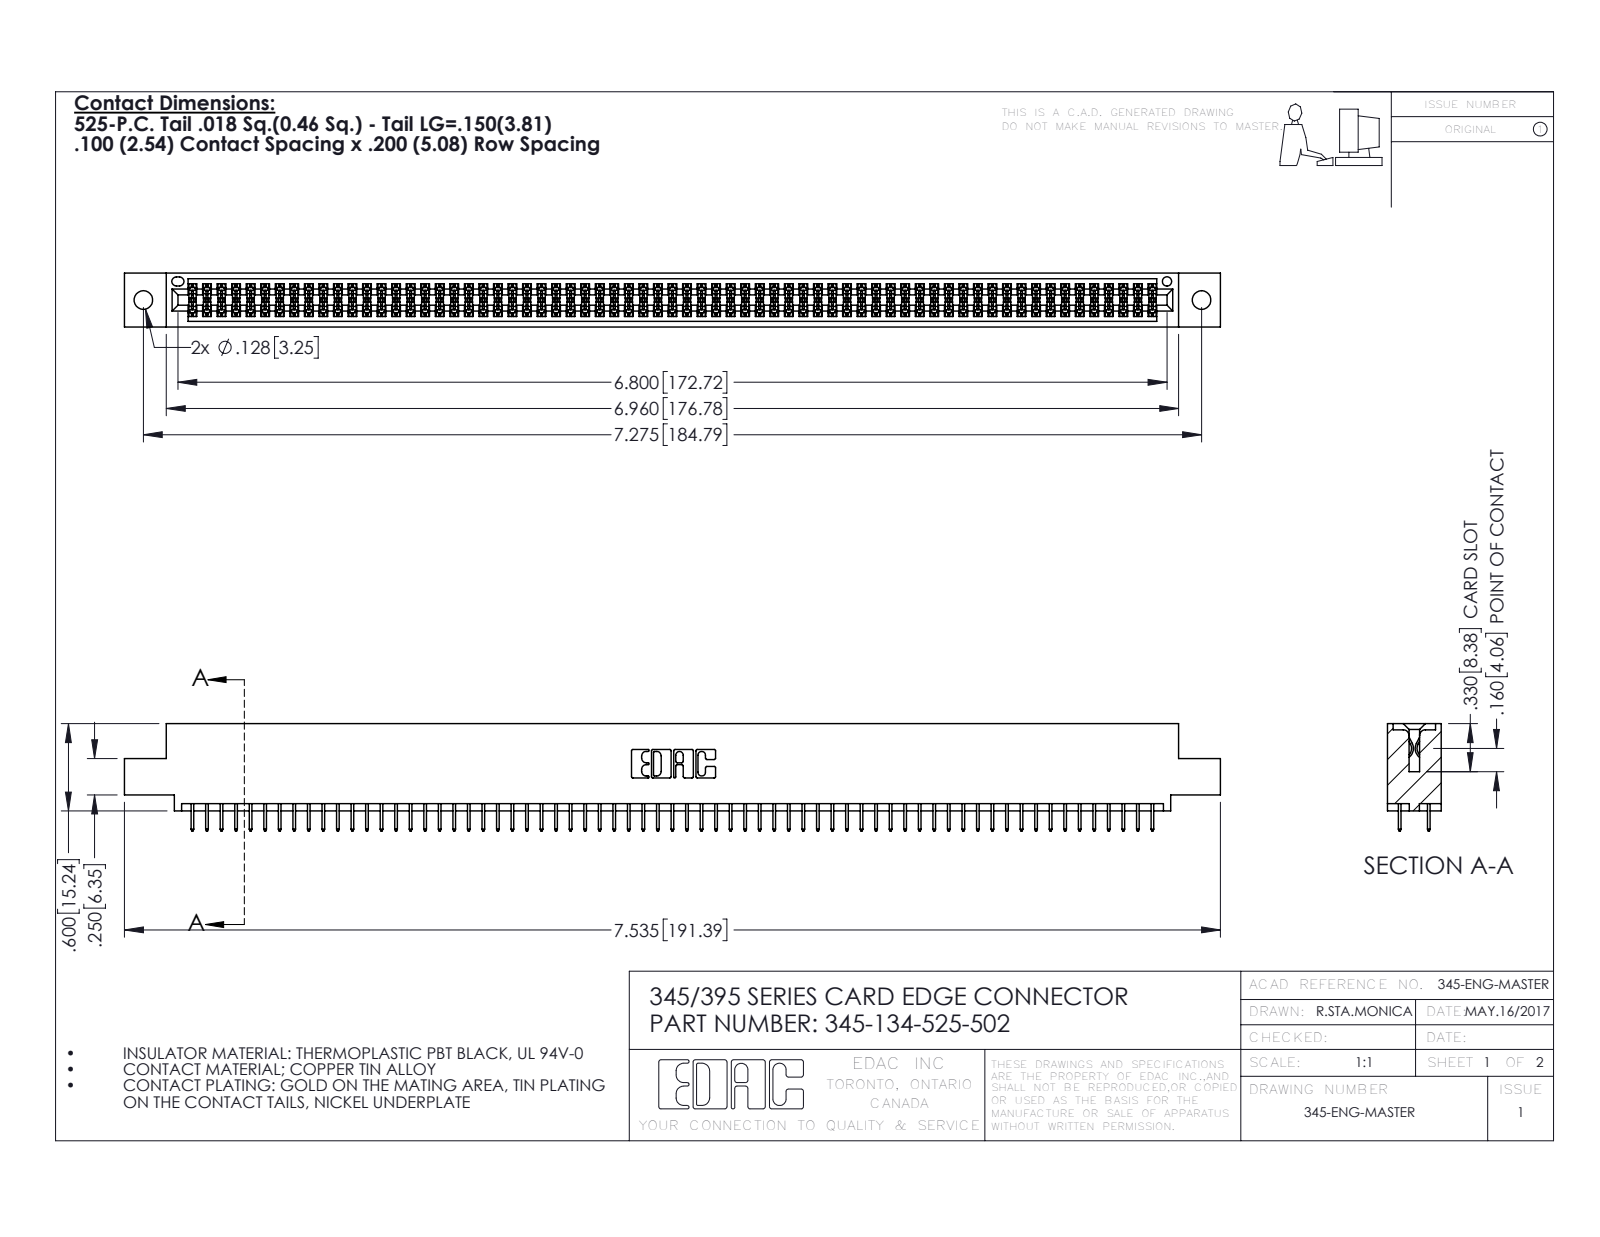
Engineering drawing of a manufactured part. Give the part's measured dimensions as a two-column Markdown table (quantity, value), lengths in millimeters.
| quantity | value |
| --- | --- |
| part name | 345-134-525-502; 345-292-001_345-293-125; 345 Part_0.110 Offset - 0.128 Dia |
| STEP written by | SolidWorks 2020 (CONFIG_CONTROL_DESIGN) |
| units | millimeters |
| bodies | 135 solids, 7366 faces (5310 planar, 2056 cylindrical, 0 other) |
| overall size | 191.4 × 18.7 × 9.4 |
| volume | 18 500 mm³ |
| surface area | 26 970 mm² |
| round holes (diameter × count) | 3.3 × 2, 1.6 × 1 |
| partial cylindrical surfaces (radius × count) | 0.2 × 201, 0.3 × 22, 0.2 × 6, 0.8 × 6, 0.7 × 3, 0.4 × 2, 0.5 × 2, 0.6 × 2 |
| main face-to-face distances | 1.8, 7.6, 5.1, 9.4, 2.5, 6.9, 0.6, 5.7, 1.8, 4.4 |
| hole center spacings | 6.9, 178.8, 184.8 |
